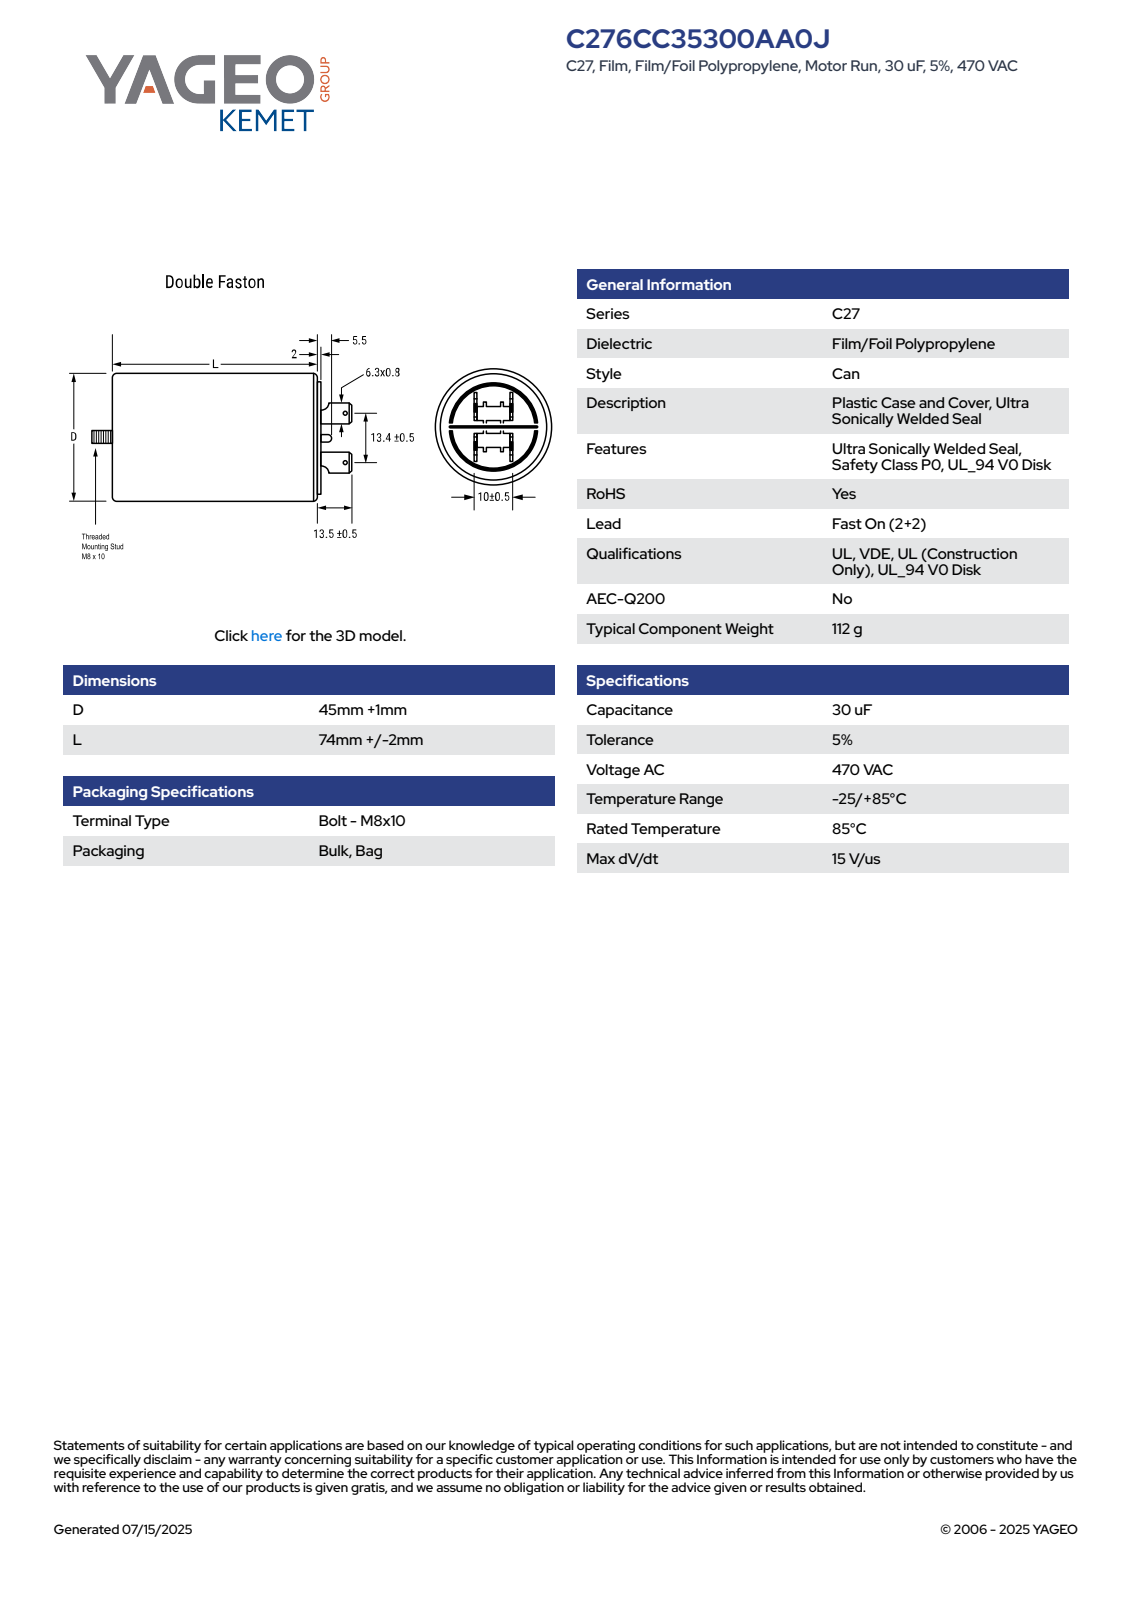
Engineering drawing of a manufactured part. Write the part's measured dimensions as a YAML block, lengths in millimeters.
part_name: "CFM_C27DF_45X74_D46L76"
step_written_by: "SolidWorks 2014 (AUTOMOTIVE_DESIGN)"
units: millimeters
bodies: {solids: 1, faces: 137, planar: 49, cylindrical: 53, other: 35}
overall_size: [100, 46, 46]
volume: 128815
surface_area: 15429
round_holes:
  - {diameter: 1.2, count: 2}
round_bosses_or_shafts:
  - {diameter: 46, count: 1}
  - {diameter: 35.38, count: 1}
  - {diameter: 8, count: 1}
partial_cylinders:
  - {radius: 0.25, count: 9}
  - {radius: 4, count: 2}
  - {radius: 22.99, count: 1}
face_to_face_distances: [78, 76, 2, 0.8, 9.7, 10.5, 8.9, 0.5, 10, 86]
hole_center_spacings: [13.9]
